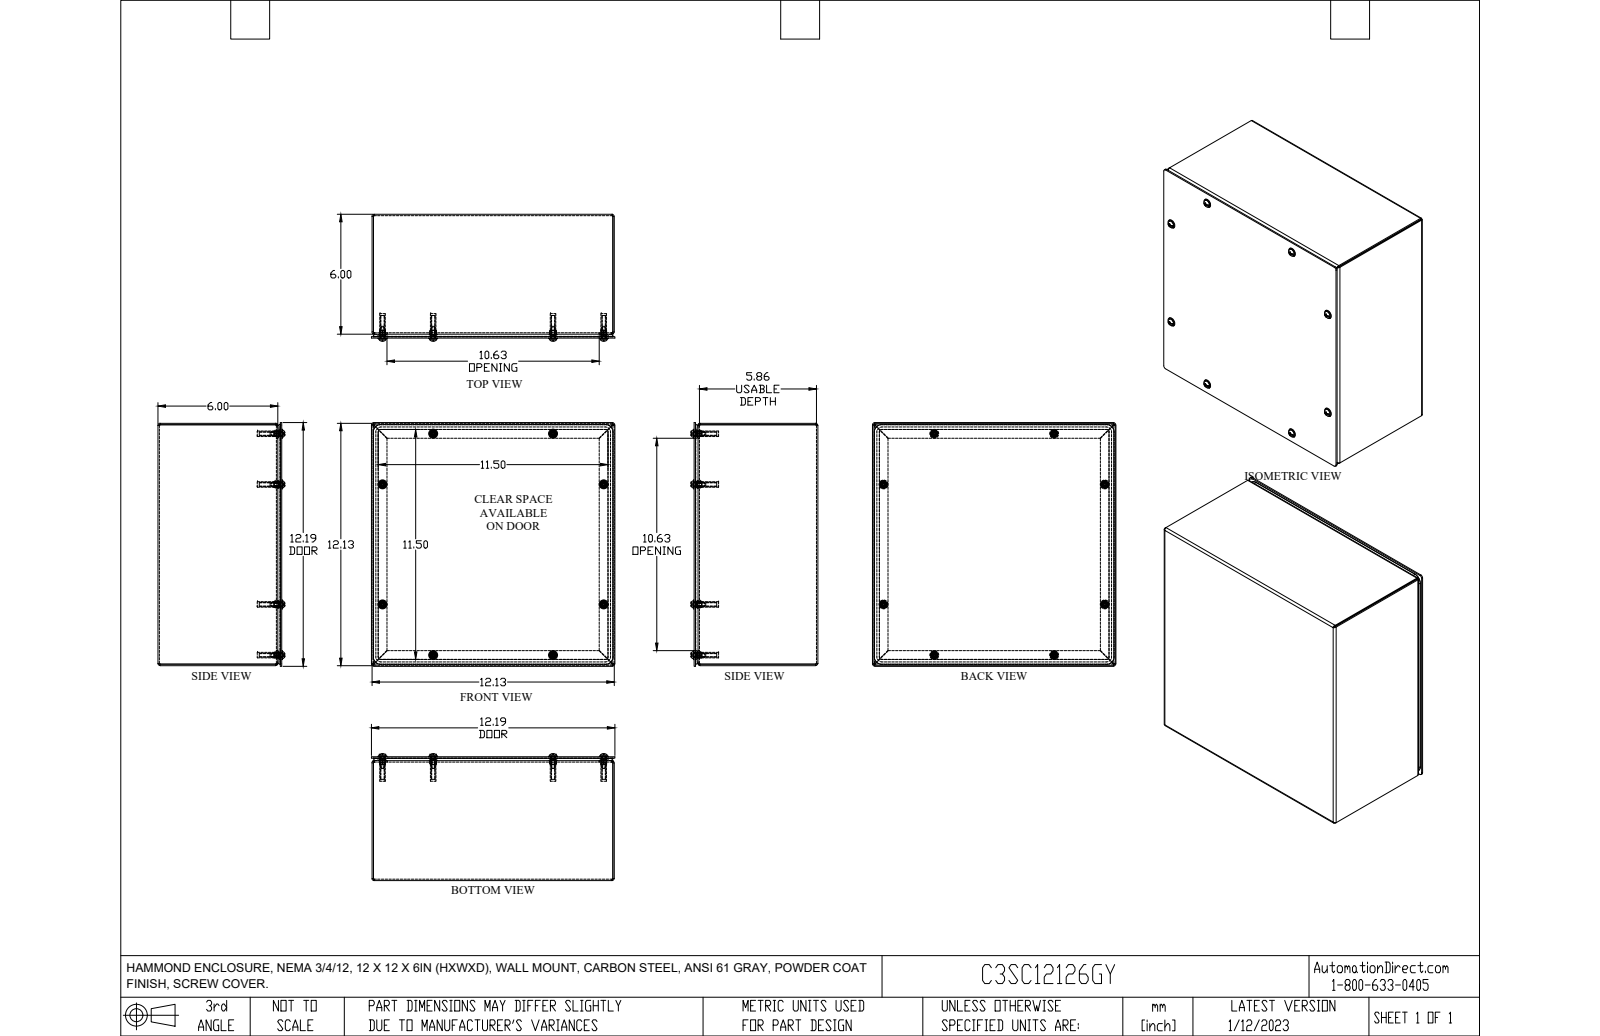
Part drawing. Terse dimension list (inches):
name: C3SC12126GY
written by: SolidWorks 2021 (AUTOMOTIVE_DESIGN)
unit: in
bodies: 27 solids, 780 faces (480 planar, 152 cylindrical, 148 other)
size: 12.188 × 12.188 × 6.347
volume: 44.53 in³; area: 1 301 in²
holes: 8× ⌀0.159, 8× ⌀0.16, 8× ⌀0.25
bosses: 8× ⌀0.44, 8× ⌀0.39, 8× ⌀0.24, 8× ⌀0.19, 8× ⌀0.148, 4× ⌀0.275, 4× ⌀0.275
rounds: 8× R0.04, 8× R0.11, 8× R0.125, 8× R0.16, 4× R0.126, 4× R0.374
face distances: 0.07, 0.072, 6.125, 6.127, 6.197, 6.055, 12.13, 12.06, 12.06, 11.99
hole spacings: 8.906, 3.589, 6, 11.075, 12.074, 12.596
